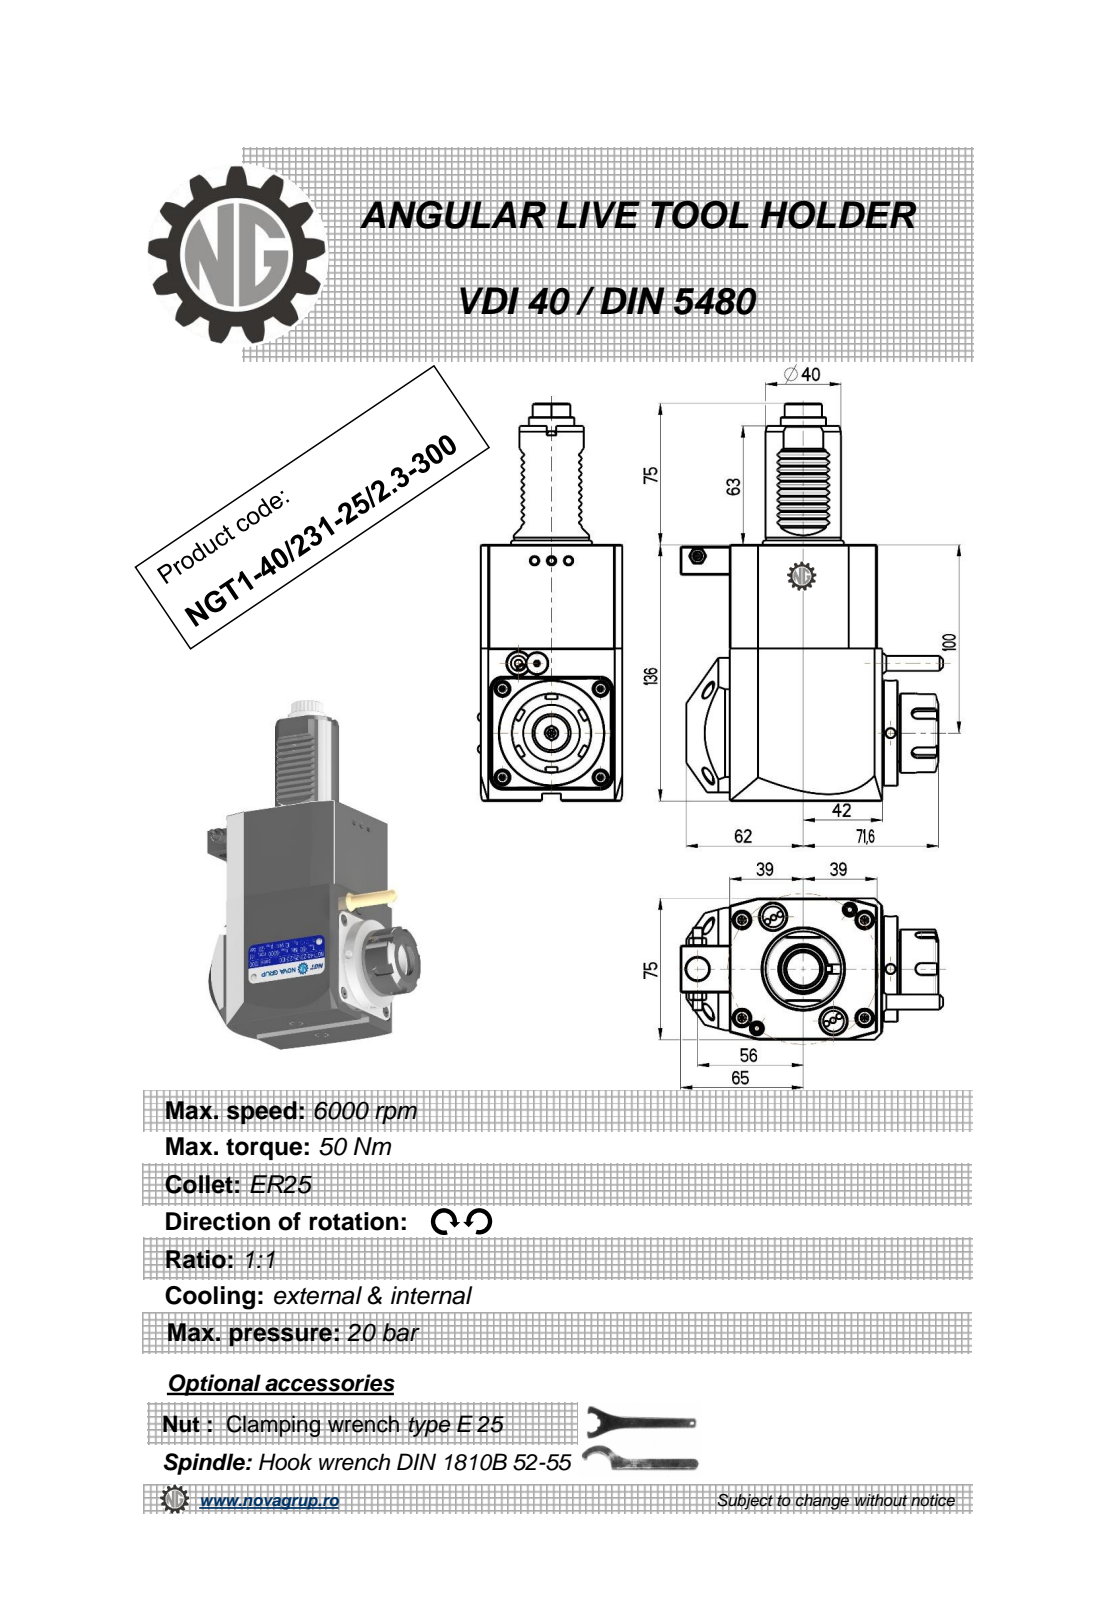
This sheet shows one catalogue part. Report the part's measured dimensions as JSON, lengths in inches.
{"part_name": "NGT1_40_231_25_2_3_100", "step_written_by": "PRO/ENGINEER BY PARAMETRIC TECHNOLOGY CORPORATION, 2010280 (CONFIG_CONTROL_DESIGN)", "units": "inches", "bodies": {"solids": 1, "faces": 595, "planar": 229, "cylindrical": 191, "other": 175}, "overall_size": [8.307, 5.478, 2.953], "volume_in3": 60.53, "surface_area_in2": 119.6, "round_holes": [[0.197, 3], [0.118, 1], [0.165, 1], [0.374, 1], [0.472, 1], [0.799, 1]], "round_bosses_or_shafts": [[2.205, 1], [1.693, 1], [1.654, 1], [1.575, 1], [1.299, 1], [0.945, 1], [0.441, 1], [0.353, 1]], "partial_cylinders_radius": [[0.082, 48], [0.012, 20], [0.01, 12], [0.009, 6], [0.118, 5], [0.357, 1], [0.391, 1], [0.591, 1]], "face_to_face_distances": [2.953, 5.354, 3.071, 3.189, 0.118, 0.433, 0.315, 3.342, 0.323, 0.02], "hole_center_spacings": [1.611, 2.254, 3.602, 4.026, 5.468]}
